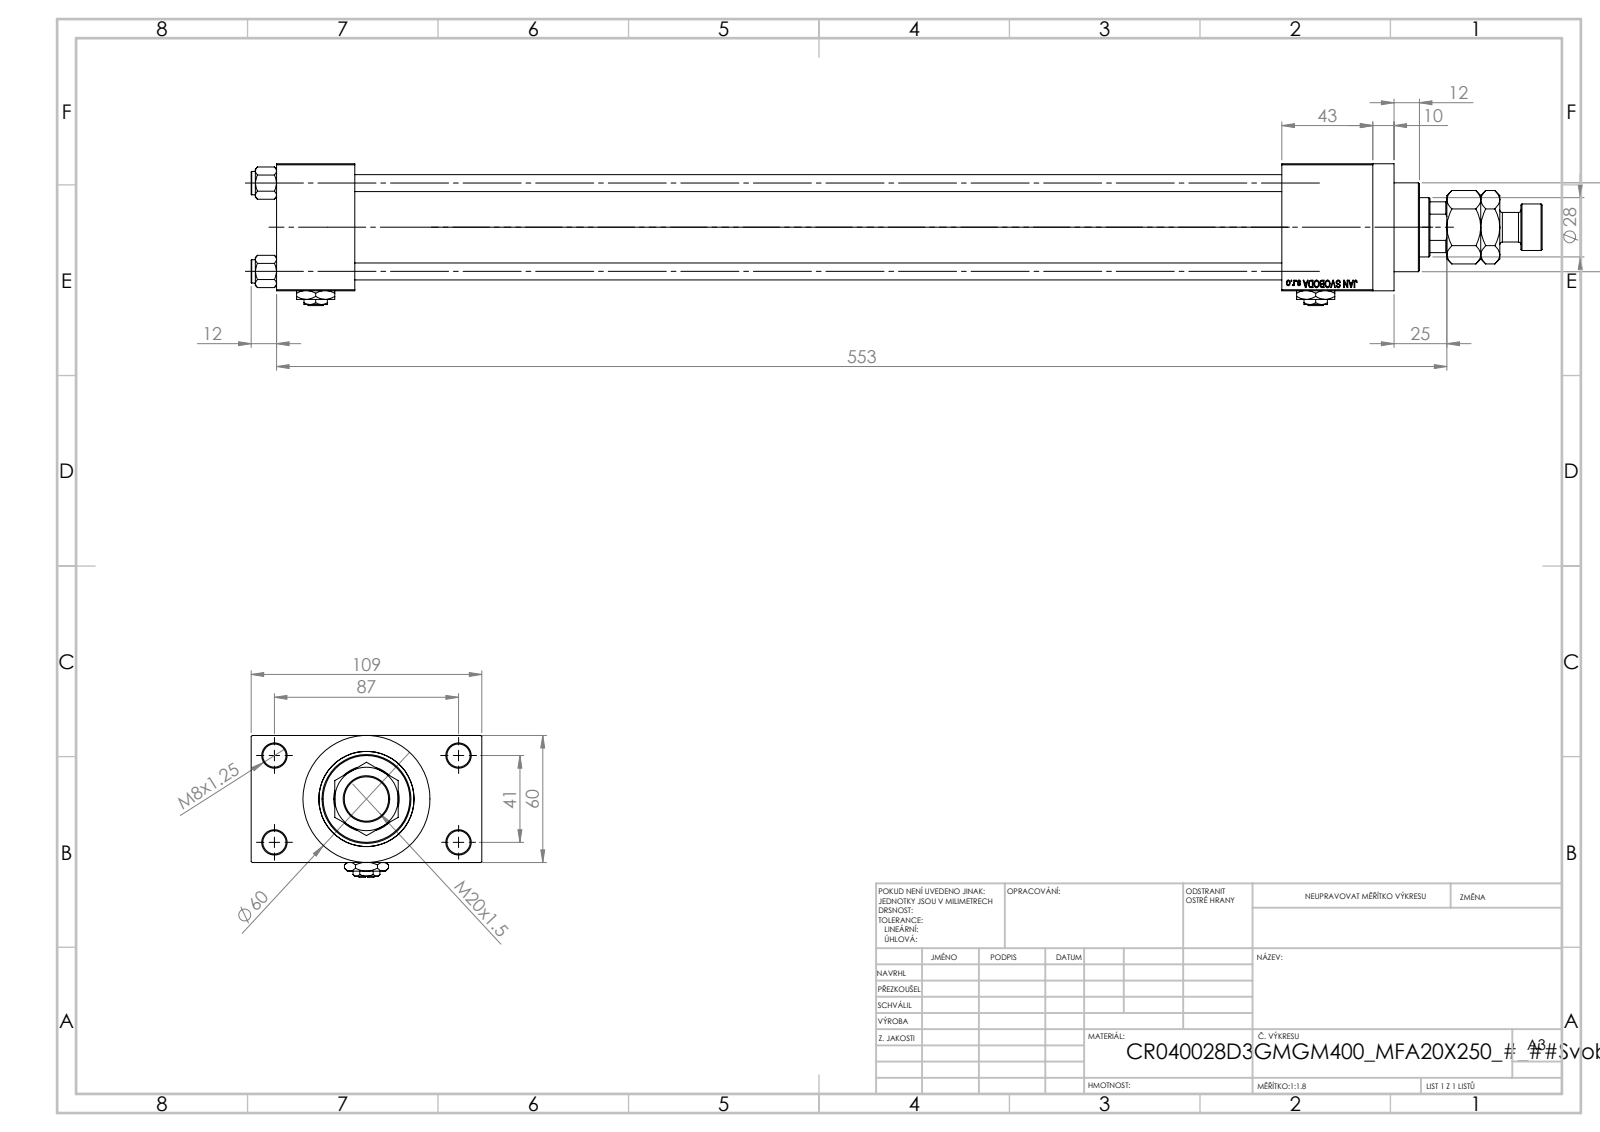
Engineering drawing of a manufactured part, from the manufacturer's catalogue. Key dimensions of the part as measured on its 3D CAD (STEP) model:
Part name (STEP PRODUCT): V215CR_VCP_D; V215CR_D_Body; Zatka_pro_OIL_PORT; NUT_M5_D (+3 more)
STEP written by: SolidWorks 2019 (CONFIG_CONTROL_DESIGN)
Units: millimetres
Bodies: 14 solids, 1257 faces (562 planar, 103 cylindrical, 592 other)
Overall size (bounding box): 610 × 109 × 67
Volume: 1 016 000 mm³ · Surface area: 311 549 mm²
Round holes (diameter × count): ⌀8 ×4, ⌀11 ×4, ⌀16.66 ×4, ⌀24 ×4, ⌀7 ×3, ⌀18.5 ×1, ⌀28 ×1, ⌀31 ×1, ⌀40 ×1, ⌀45 ×1
Round bosses / shafts (diameter × count): ⌀11 ×4, ⌀60 ×1, ⌀46 ×1, ⌀42 ×1, ⌀22 ×1, ⌀14 ×1
Partial cylindrical surfaces — rounded edges, fillets, slot ends (radius × count): R13.5 ×1
Main face-to-face distances: 60, 24.5, 438, 84.5, 37, 475, 43, 518, 481, 109
Hole centre spacings: 22.65, 29.49, 41.7, 47.15, 48.09, 64.35, 76.49, 41
